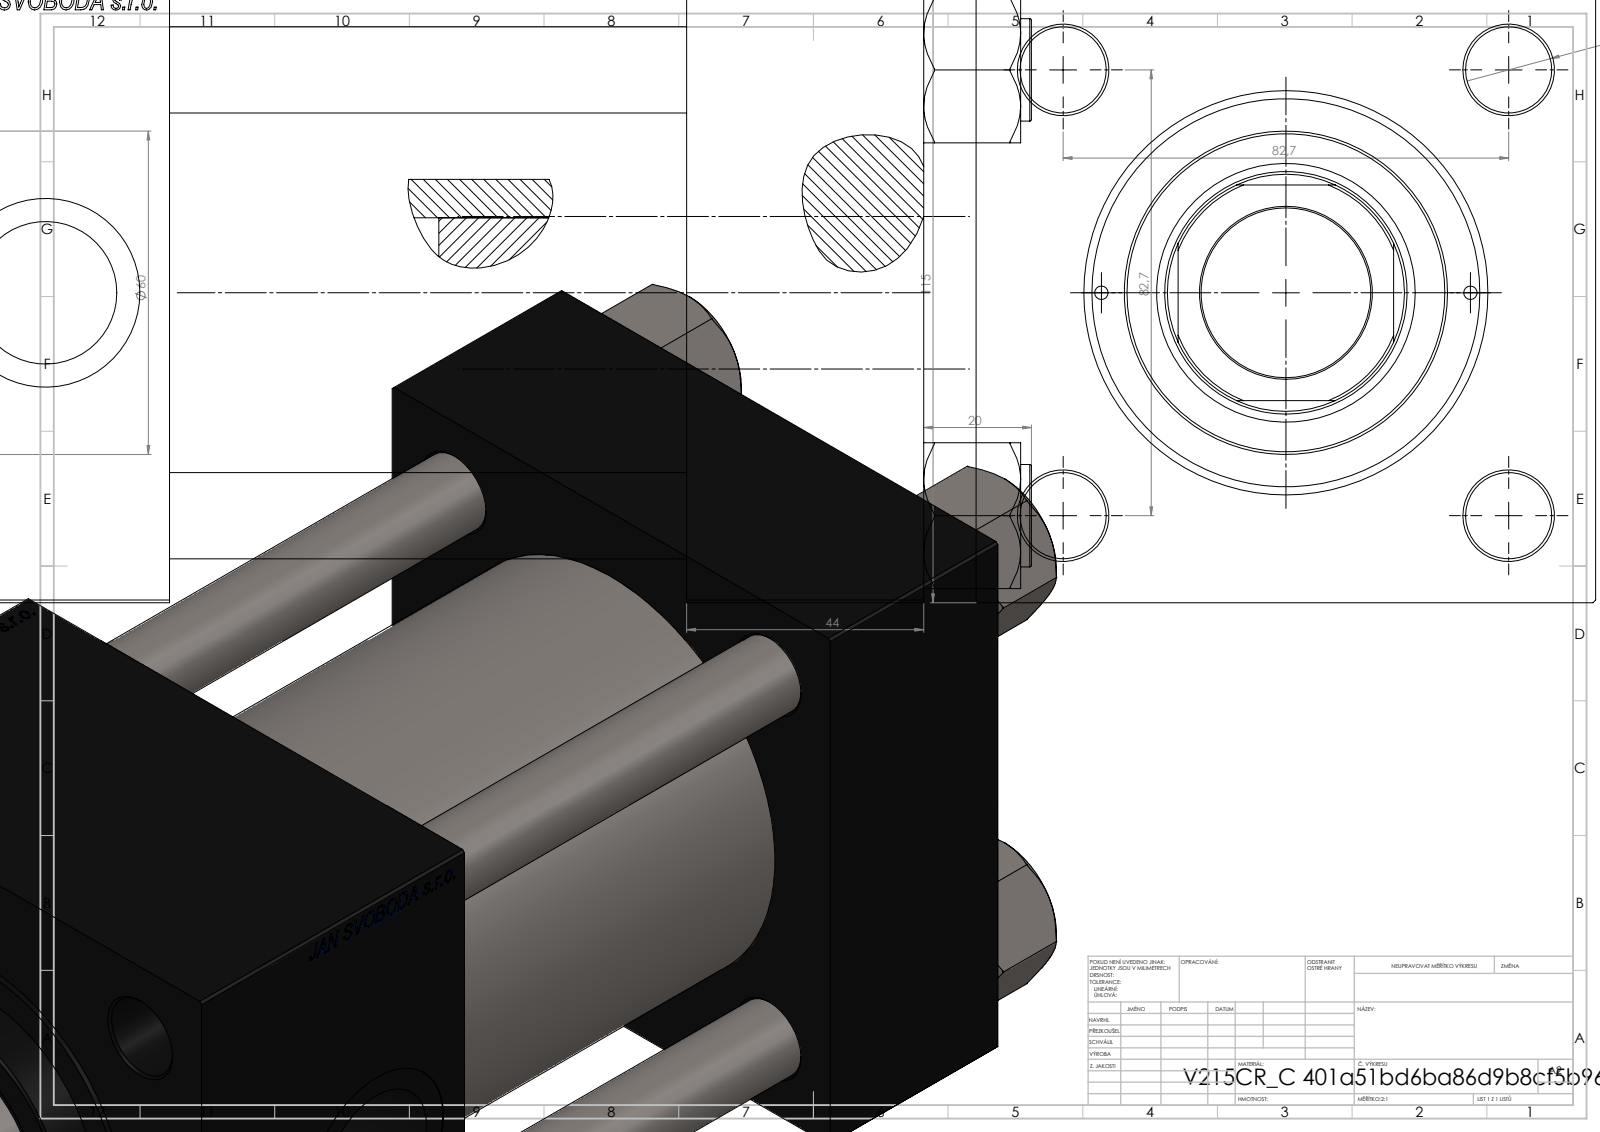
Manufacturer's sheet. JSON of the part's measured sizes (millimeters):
{"part_name": "V215_VC_A; NUT_M5_C; V215CR_C_TYCINKA; V215CR_VCP_C (+1 more)", "step_written_by": "SolidWorks 2019 (CONFIG_CONTROL_DESIGN)", "units": "millimeters", "bodies": {"solids": 11, "faces": 1202, "planar": 576, "cylindrical": 90, "other": 536}, "overall_size": [260, 115, 115], "volume_mm3": 1915000, "surface_area_mm2": 299872, "round_holes": [[16, 4], [2.5, 2], [7, 2], [26.44, 2], [35, 2], [31.5, 1], [45, 1], [48, 1], [61, 1], [72, 1], [80, 1]], "round_bosses_or_shafts": [[19, 4], [86, 1], [60, 1]], "partial_cylinders_radius": [[22, 1]], "face_to_face_distances": [115, 44, 209, 165, 140, 96, 69, 180.3, 136.3, 40.3], "hole_center_spacings": [41.96, 58.48, 82.7, 86.17, 34.25, 116.96, 68.5, 141]}
